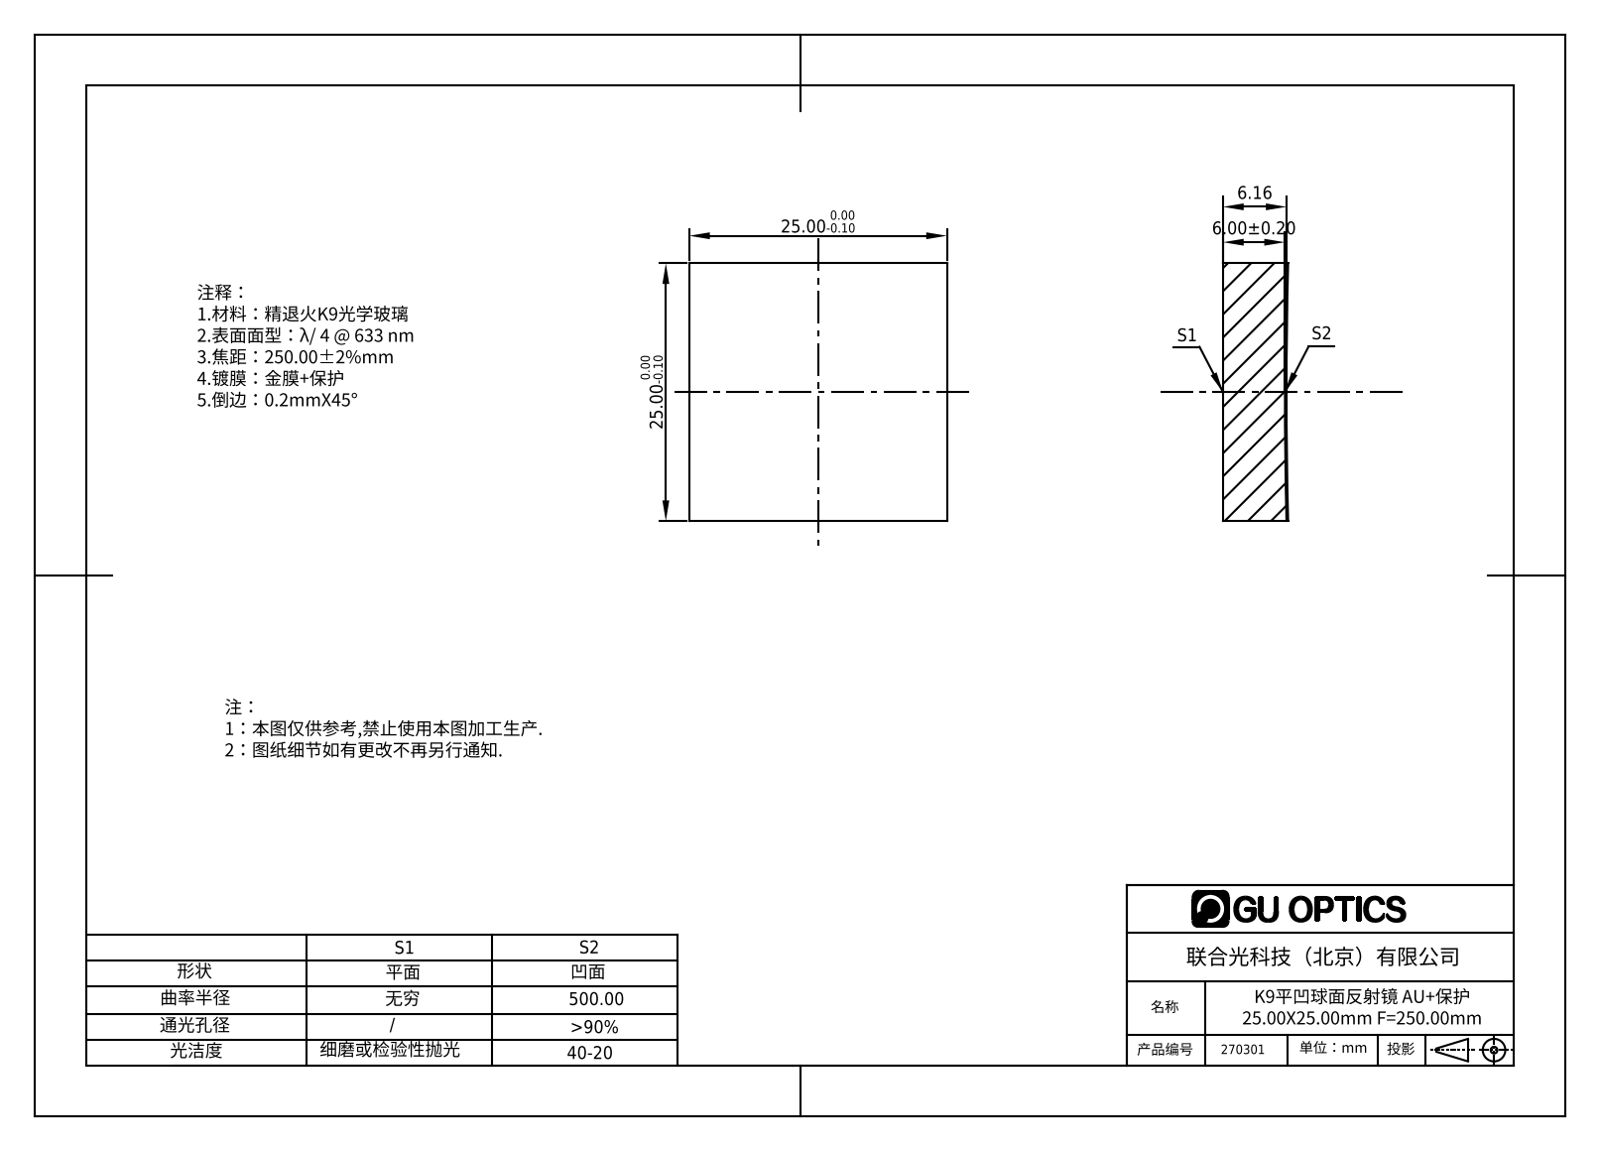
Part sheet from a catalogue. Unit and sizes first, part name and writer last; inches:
Units: inches
Overall size (bounding box): 0.984 × 0.984 × 0.248
Main face-to-face distances: 0.984
Volume: 0.233 in³ · Surface area: 2.9 in²
Bodies: 1 solid, 7 faces (5 planar, 0 cylindrical, 2 other)
Part name (STEP PRODUCT): 270041
STEP written by: SolidWorks 2019 (AUTOMOTIVE_DESIGN)
